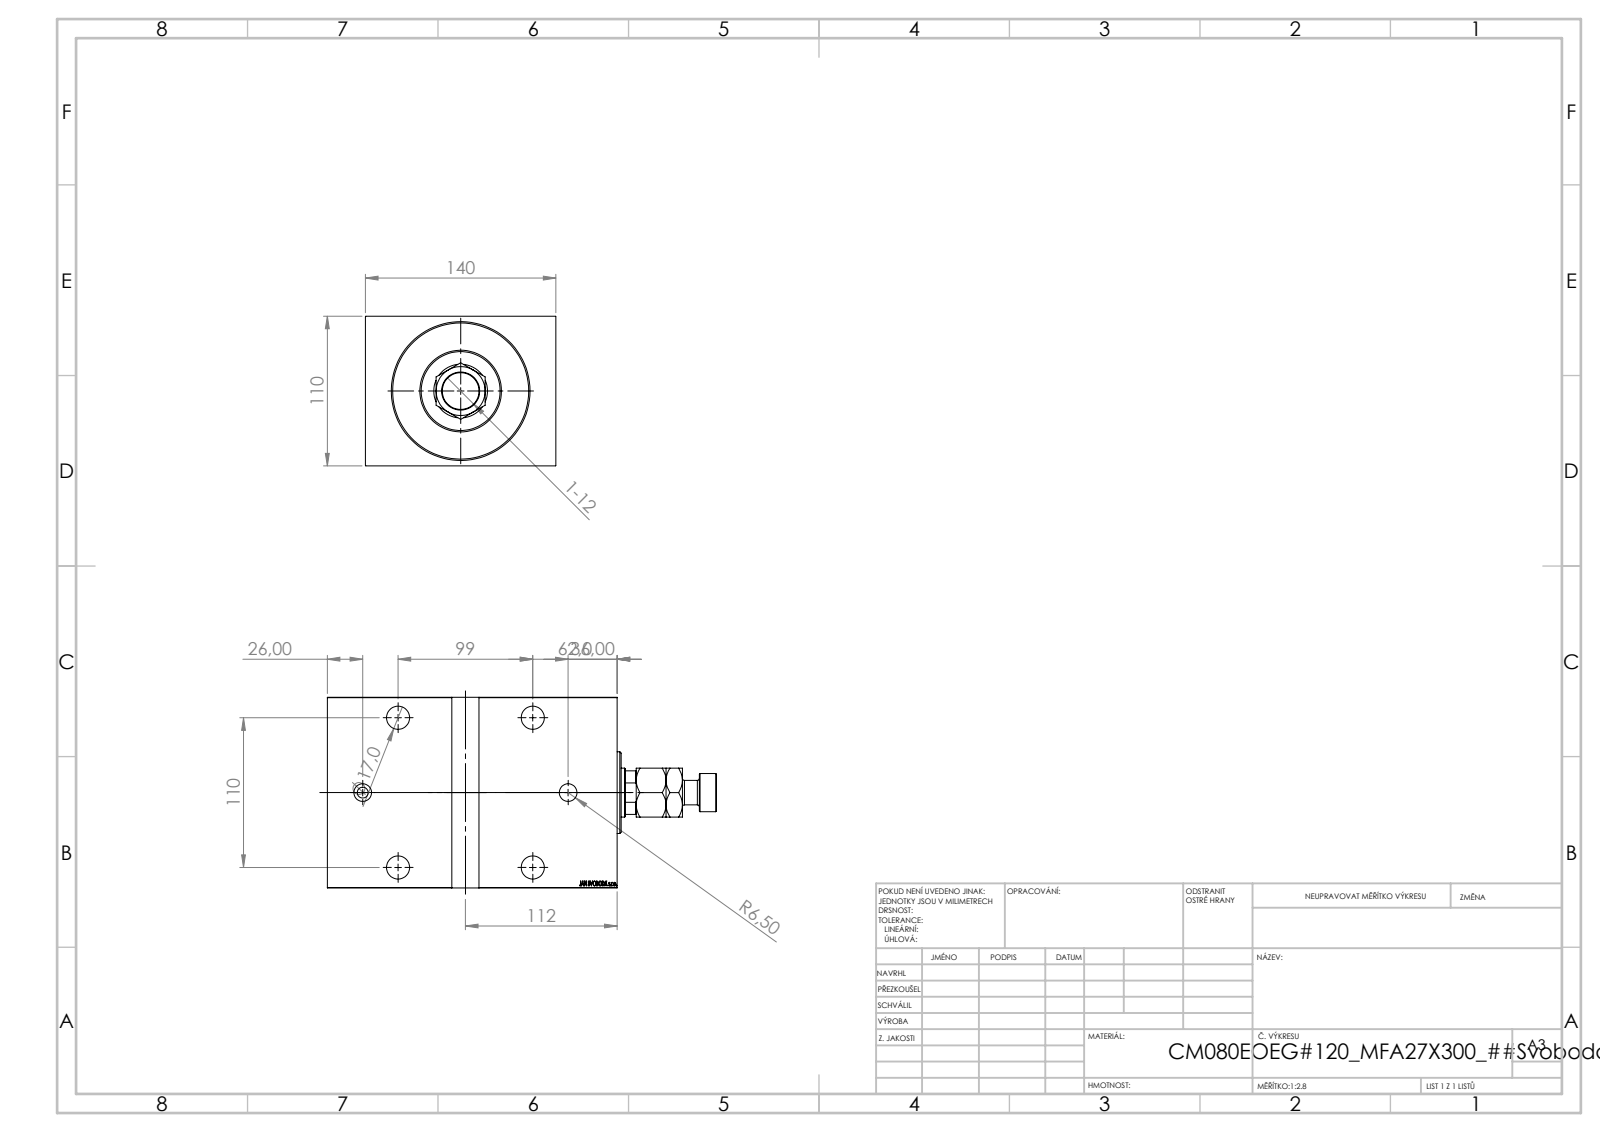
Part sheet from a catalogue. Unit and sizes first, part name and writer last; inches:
Units: inches
Overall size (bounding box): 11.26 × 5.512 × 4.331
Round holes (diameter × count): ⌀0.669 ×4, ⌀0.984 ×4, ⌀0.512 ×2, ⌀1.004 ×1, ⌀1.417 ×1, ⌀1.555 ×1, ⌀3.15 ×1, ⌀3.937 ×1
Round bosses / shafts (diameter × count): ⌀3.228 ×1, ⌀2.362 ×1, ⌀1.102 ×1, ⌀0.709 ×1, ⌀0.315 ×1
Partial cylindrical surfaces — rounded edges, fillets, slot ends (radius × count): R0.689 ×1
Main face-to-face distances: 4.331, 5.512, 8.386, 0.827, 7.559, 0.197, 8.189, 7.362, 3.11, 7.732
Hole centre spacings: 2.395, 5.377, 3.898, 4.331, 5.826, 5.945
Volume: 166 in³ · Surface area: 441.6 in²
Bodies: 4 solids, 901 faces (425 planar, 50 cylindrical, 426 other)
Part name (STEP PRODUCT): V450CM_VC_B; V450CM_E_Body; V450CM_E_VCP; MFA
STEP written by: SolidWorks 2019 (CONFIG_CONTROL_DESIGN)
